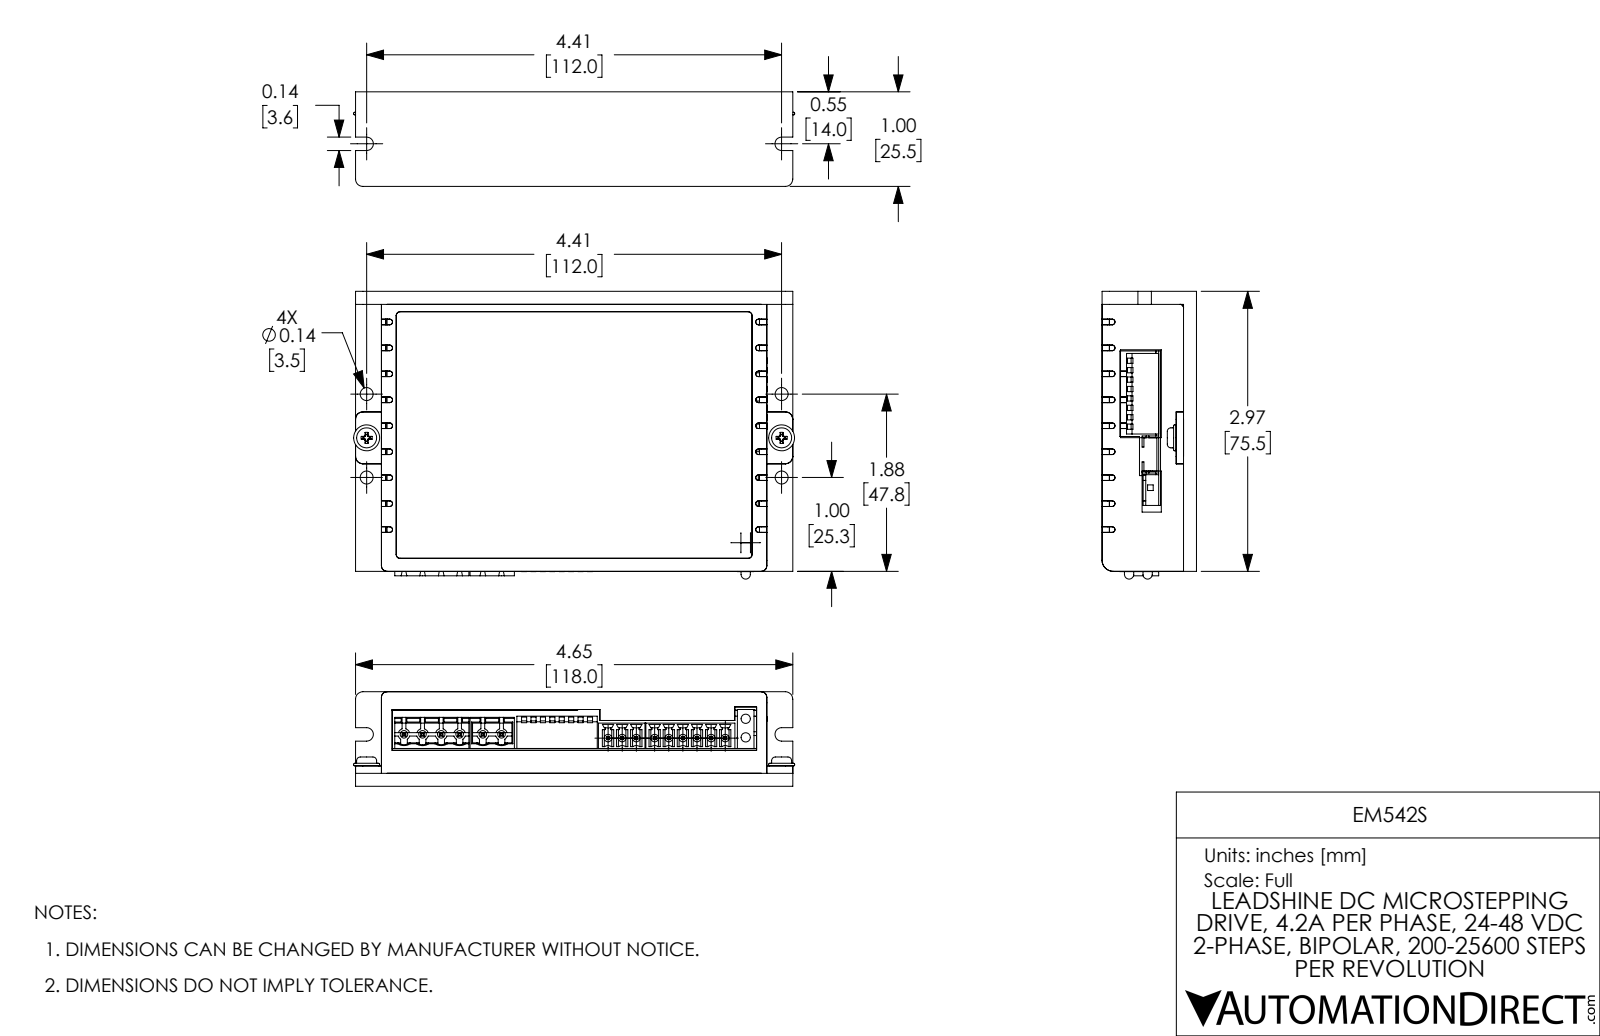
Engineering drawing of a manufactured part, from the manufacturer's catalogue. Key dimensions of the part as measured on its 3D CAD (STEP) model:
Part name (STEP PRODUCT): EM542S_V3
STEP written by: SolidWorks 2017 (AUTOMOTIVE_DESIGN)
Units: inches
Bodies: 15 solids, 1923 faces (1518 planar, 349 cylindrical, 56 other)
Overall size (bounding box): 4.685 × 3.055 × 1.004
Volume: 6.101 in³ · Surface area: 150.9 in²
Round holes (diameter × count): ⌀0.08 ×6, ⌀0.138 ×6
Round bosses / shafts (diameter × count): ⌀0.08 ×9, ⌀0.276 ×2, ⌀0.213 ×2, ⌀0.118 ×2, ⌀0.098 ×2, ⌀0.093 ×2, ⌀0.016 ×2
Partial cylindrical surfaces — rounded edges, fillets, slot ends (radius × count): R0.03 ×36, R0.039 ×10, R0.06 ×9, R0.061 ×6, R0.063 ×6, R0.079 ×6, R0.11 ×6, R0.059 ×4
Main face-to-face distances: 0.071, 0.138, 0.079, 0.787, 0.858, 0.925, 0.996, 0.602, 0.524, 0.402
Hole centre spacings: 4.409, 0.198, 0.421, 0.465, 0.641, 0.886, 4.43, 4.434
